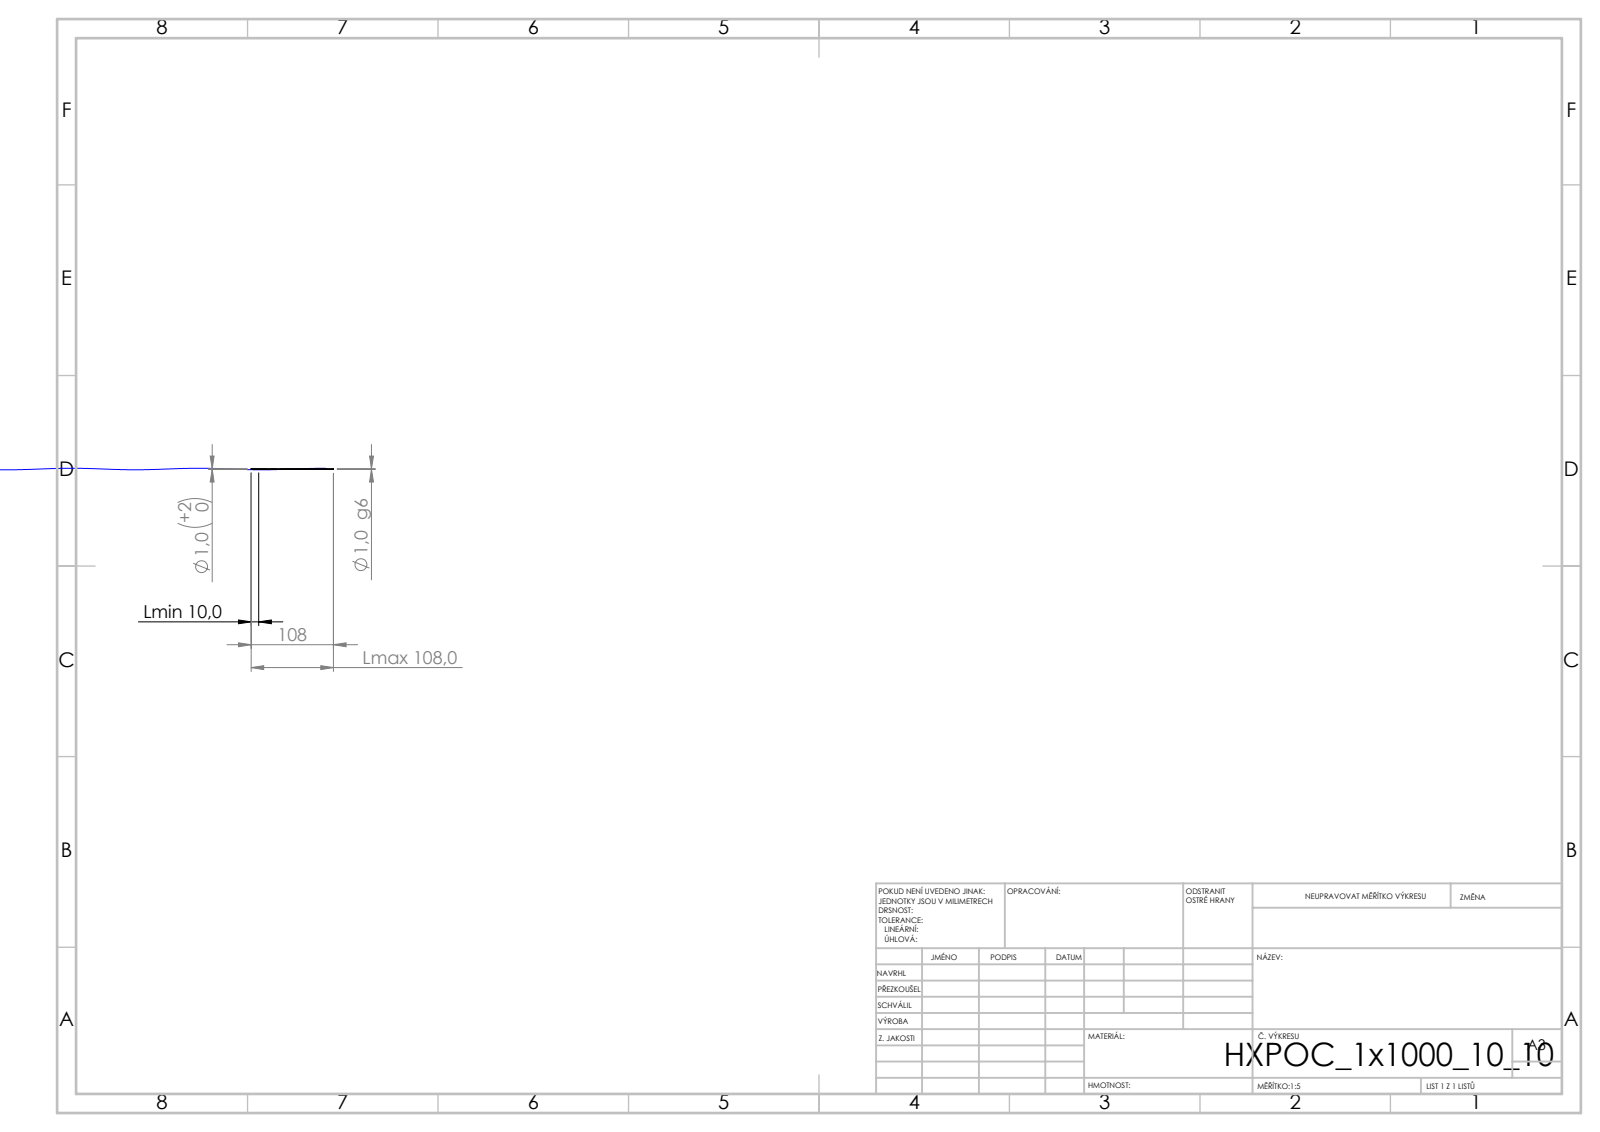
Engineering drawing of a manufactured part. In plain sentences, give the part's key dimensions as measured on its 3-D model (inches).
Its 3-D file was written by "SolidWorks 2019 (CONFIG_CONTROL_DESIGN)". It is 1 solid with 4 faces: 2 planar, 2 cylindrical and 0 other. Overall it measures 4.252 by 0.039 by 0.039 inches. Its volume is 0.005 cubic inches and its surface area 0.529 square inches. Round bosses or shafts: 1 of diameter 0.039. The main face-to-face distances are 4.252.
